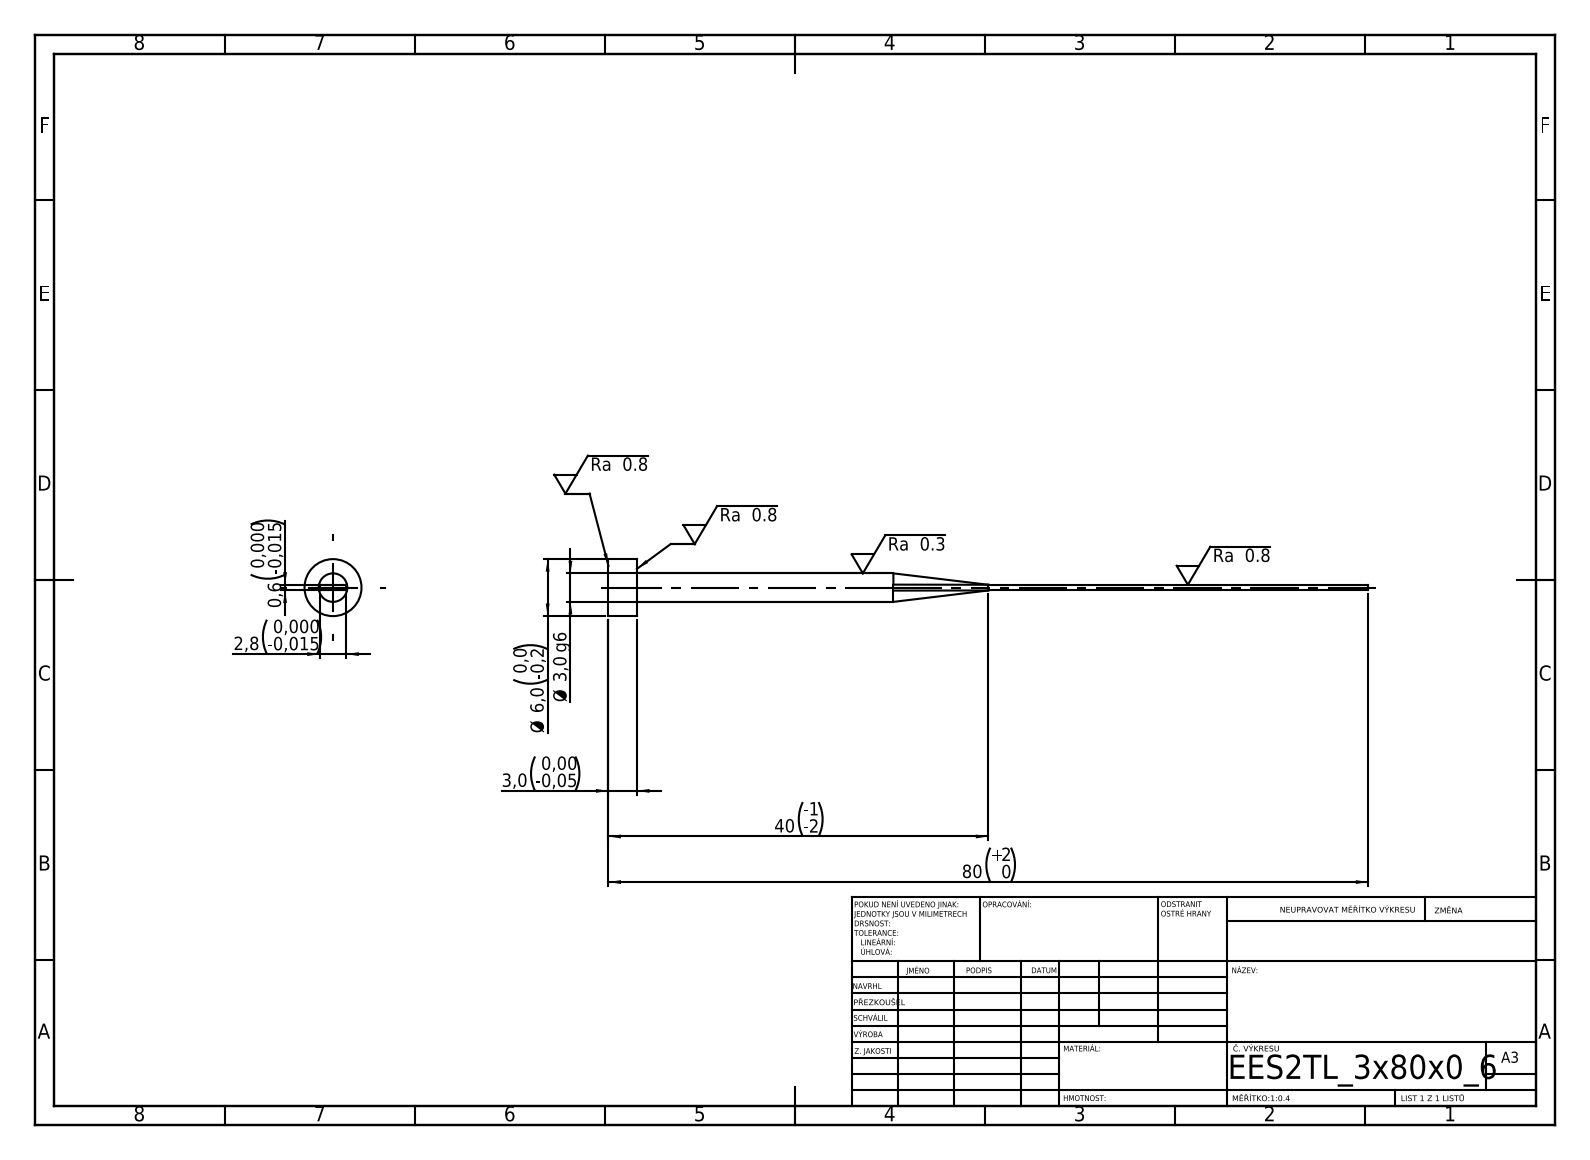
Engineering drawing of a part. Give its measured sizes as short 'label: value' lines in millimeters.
written by: SolidWorks 2019 (CONFIG_CONTROL_DESIGN)
unit: mm
bodies: 1 solid, 15 faces (7 planar, 4 cylindrical, 4 other)
size: 80 × 6 × 6
volume: 385 mm³; area: 712 mm²
bosses: 1× ⌀6, 1× ⌀3
face distances: 0.6, 2.8, 3, 80, 77
